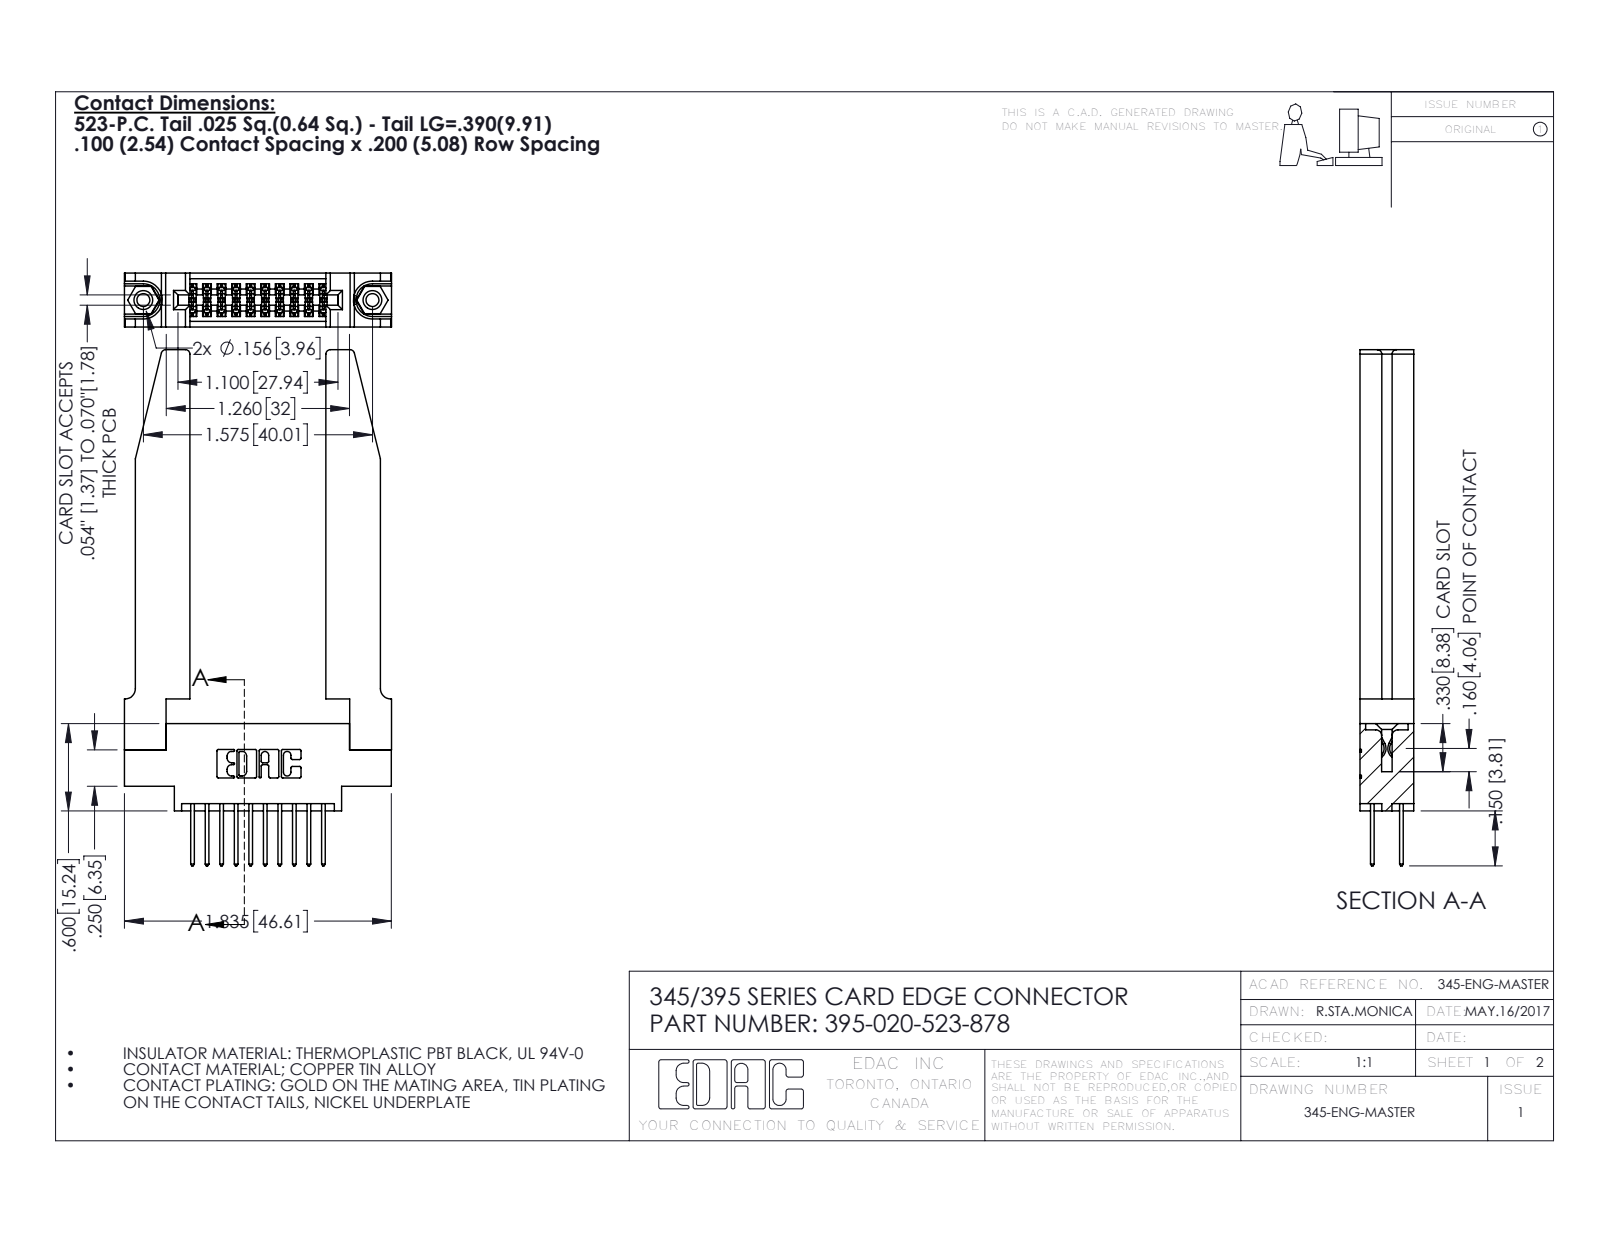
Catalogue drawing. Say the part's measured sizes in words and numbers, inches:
The part is named "345-220-078_345-220-078; 395-020-523-878; 345-250-001_345-250-001-102; 345 Part_0.170 Offset - 0.156 Dia-TH (+1 more)". Its 3-D file was written by "SolidWorks 2016 (CONFIG_CONTROL_DESIGN)". It is 25 solids with 1364 faces: 886 planar, 426 cylindrical and 52 other. Overall it measures 3.547 by 1.836 by 0.37 inches. Its volume is 0.728 cubic inches and its surface area 19.68 square inches. Round holes: 2 of diameter 0.089, 2 of diameter 0.125, 2 of diameter 0.156, 1 of diameter 0.064. Round bosses or shafts: 2 of diameter 0.155. Partial cylindrical surfaces (rounded edges, fillets, slot ends): 30 of radius 0.006, 22 of radius 0.01, 20 of radius 0.01, 8 of radius 0.03, 6 of radius 0.007, 6 of radius 0.031, 3 of radius 0.026, 2 of radius 0.014. The main face-to-face distances are 0.37, 0.072, 0.298, 0.148, 0.15, 0.22, 0.077, 0.2, 0.123, 0.098. The hole center spacings are 0.27, 1.344, 1.575.
